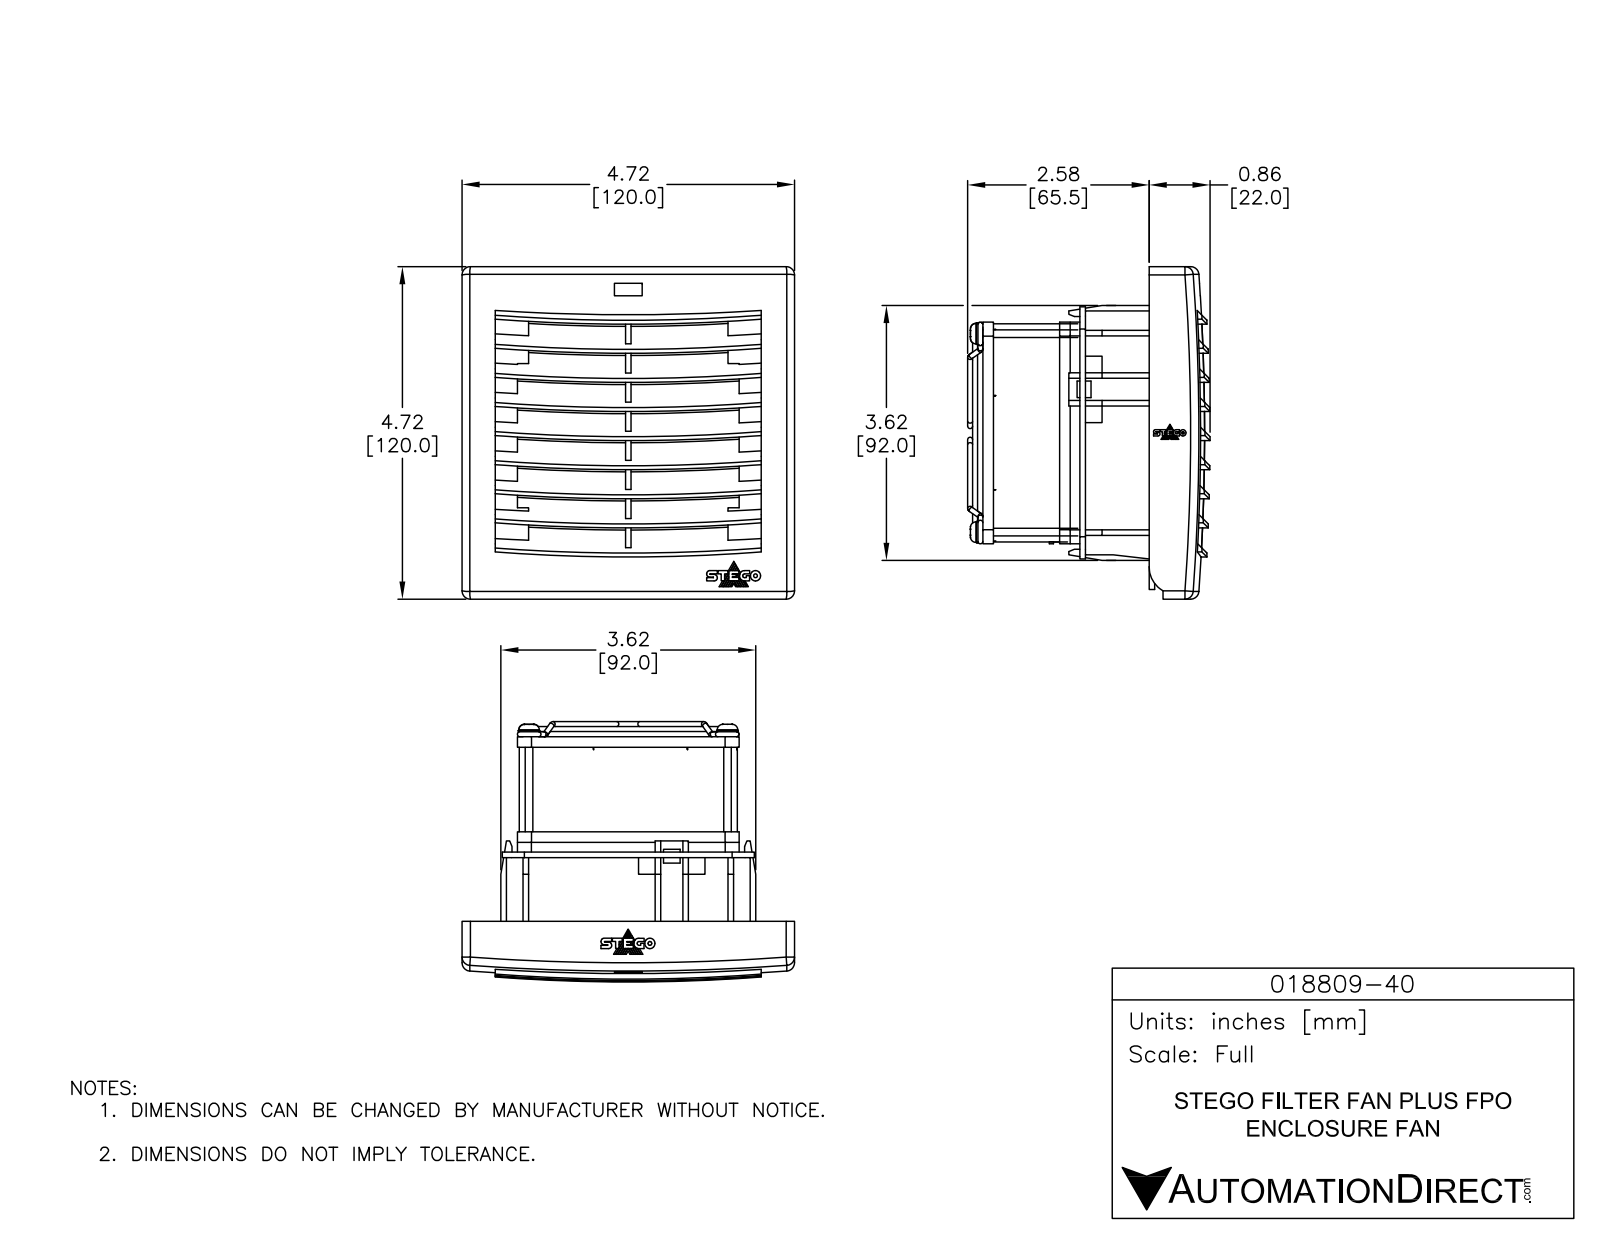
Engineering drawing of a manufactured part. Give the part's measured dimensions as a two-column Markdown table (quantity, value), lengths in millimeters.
| quantity | value |
| --- | --- |
| part name | 018809-40 |
| STEP written by | SolidWorks 2018 (AUTOMOTIVE_DESIGN) |
| units | millimeters |
| bodies | 1 solid, 486 faces (273 planar, 205 cylindrical, 8 other) |
| overall size | 120 × 120 × 95 |
| volume | 320 700 mm³ |
| surface area | 127 500 mm² |
| round holes (diameter × count) | 5.5 × 4, 17 × 1, 29.3 × 1, 41.5 × 1, 50.7 × 1, 53.8 × 1, 63.4 × 1, 68 × 1, 78.2 × 1 |
| round bosses / shafts (diameter × count) | 67.6 × 1, 57.8 × 1, 54.9 × 1, 45.5 × 1, 33.3 × 1, 23.8 × 1, 21 × 1 |
| partial cylindrical surfaces (radius × count) | 219.2 × 15, 33.3 × 5, 2.5 × 4, 3 × 4, 13.7 × 1, 19 × 1, 21.1 × 1, 43.6 × 1 |
| main face-to-face distances | 8, 1.5, 2.3, 89.7, 16.1, 9.5, 14, 16.3, 103.7, 106 |
| hole center spacings | 52.9, 74.8, 105.8 |
